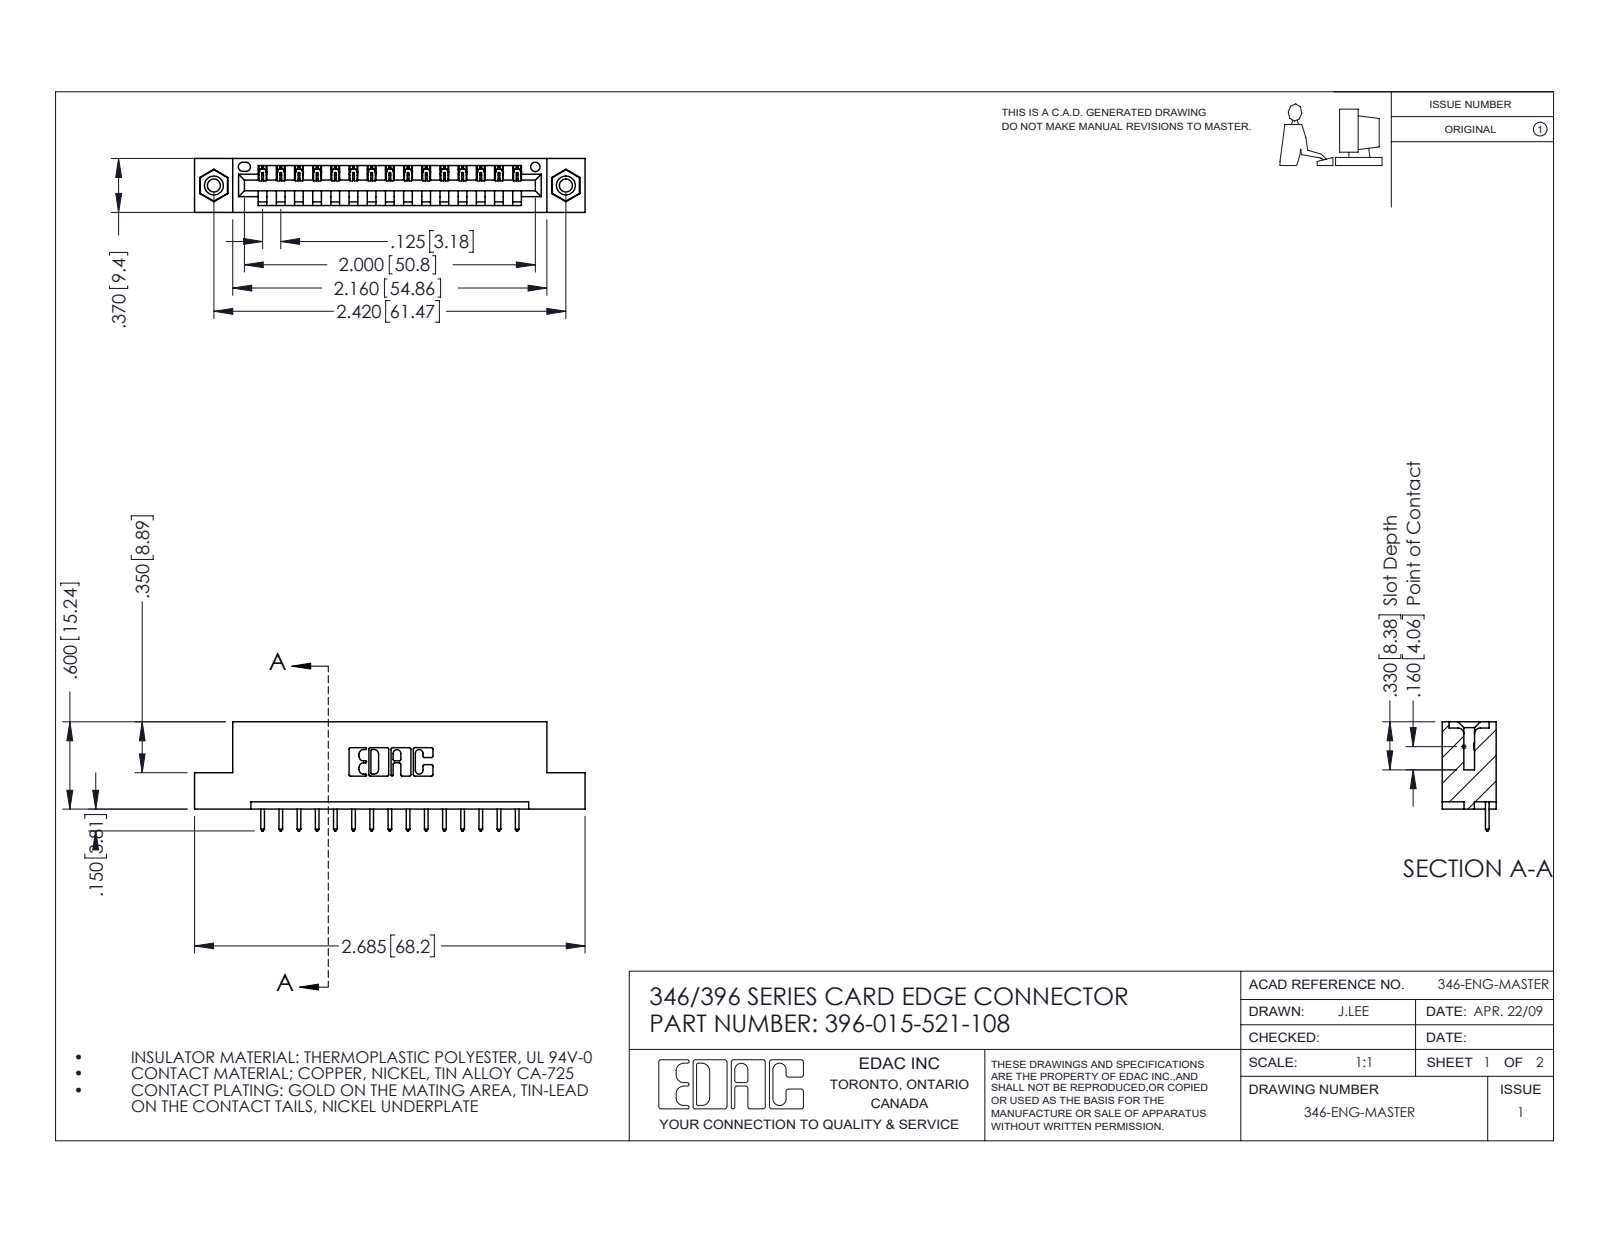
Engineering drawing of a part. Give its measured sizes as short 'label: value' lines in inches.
name: 345-292-001_345-293-121; 346 Part_Flush Mounting Lugs - 0.156 Dia-TI; 396-015-521-108; 345-250-001_345-250-003-102
written by: SolidWorks 2016 (CONFIG_CONTROL_DESIGN)
unit: in
bodies: 18 solids, 1052 faces (708 planar, 328 cylindrical, 16 other)
size: 2.685 × 0.75 × 0.37
volume: 0.384 in³; area: 11.51 in²
holes: 2× ⌀0.089, 2× ⌀0.125, 2× ⌀0.156, 1× ⌀0.064
bosses: 2× ⌀0.155
rounds: 30× R0.006, 30× R0.01, 22× R0.01, 6× R0.007, 6× R0.031, 3× R0.026, 2× R0.031, 2× R0.04
face distances: 0.25, 0.048, 0.322, 0.37, 0.072, 0.298, 0.025, 0.148, 0.222, 0.1
hole spacings: 0.246, 2.213, 2.42
